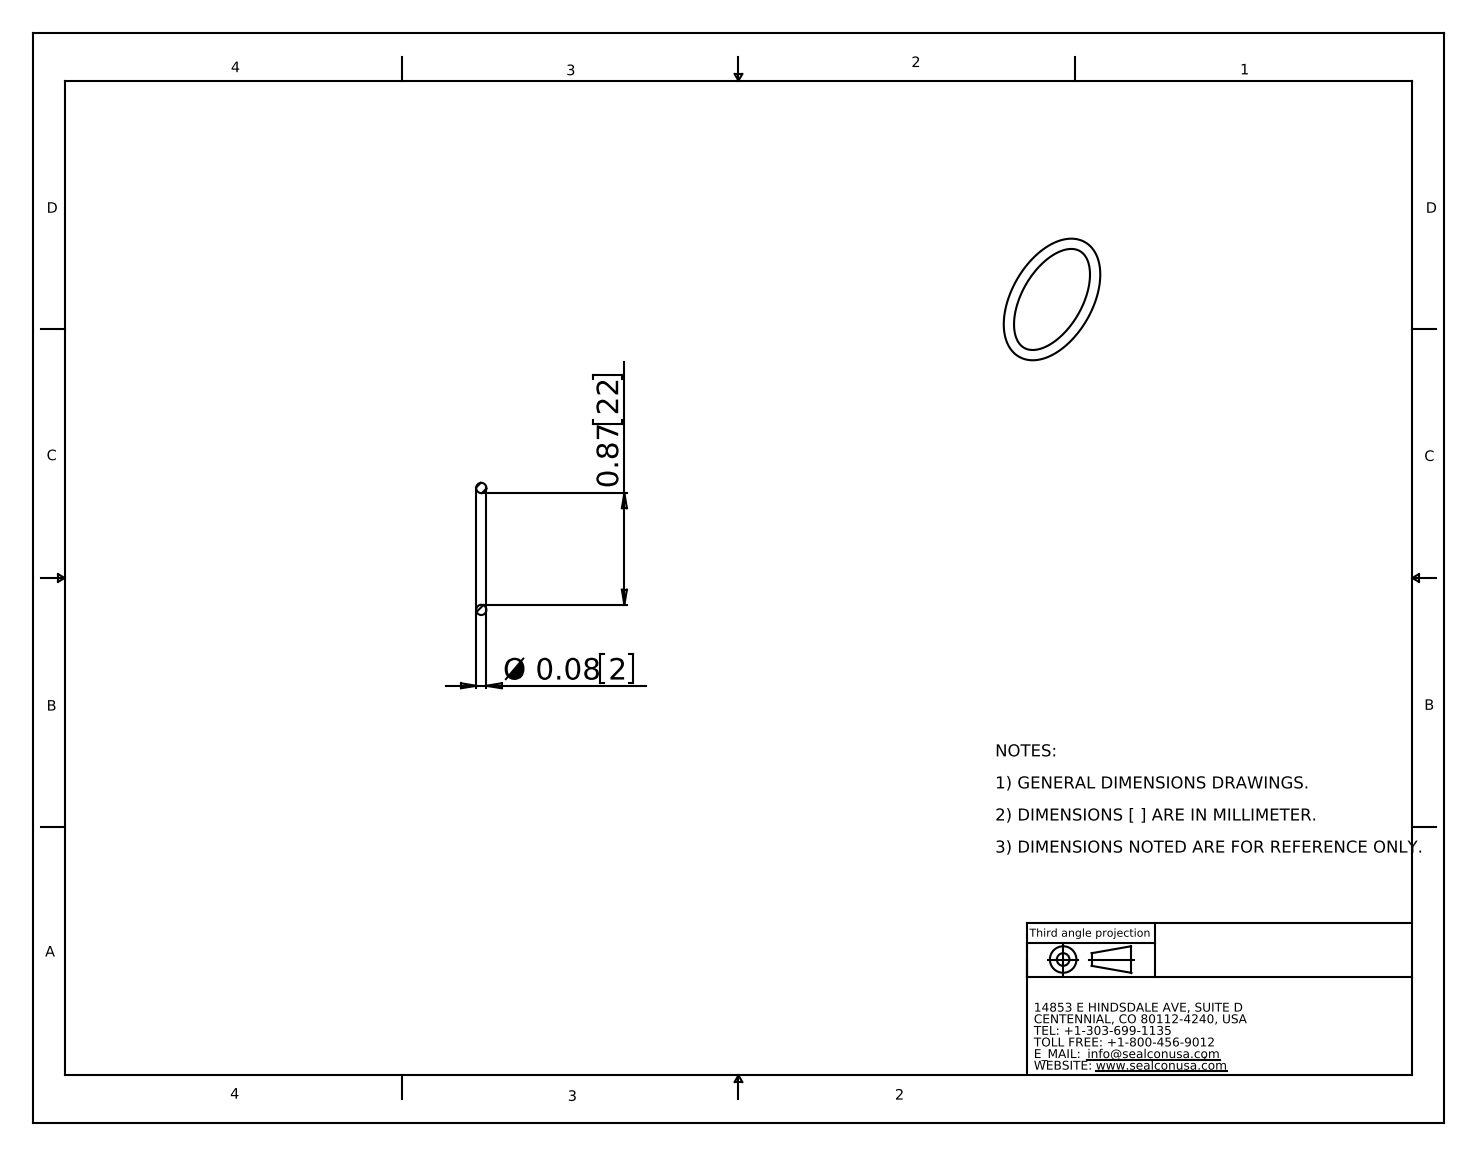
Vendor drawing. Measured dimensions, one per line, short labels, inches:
name: OM-25-SI
written by: SolidWorks 2008 (CONFIG_CONTROL_DESIGN)
unit: in
bodies: 1 solid, 4 faces (0 planar, 0 cylindrical, 4 other)
size: 1.03 × 1.03 × 0.08
volume: 0.015 in³; area: 0.75 in²
